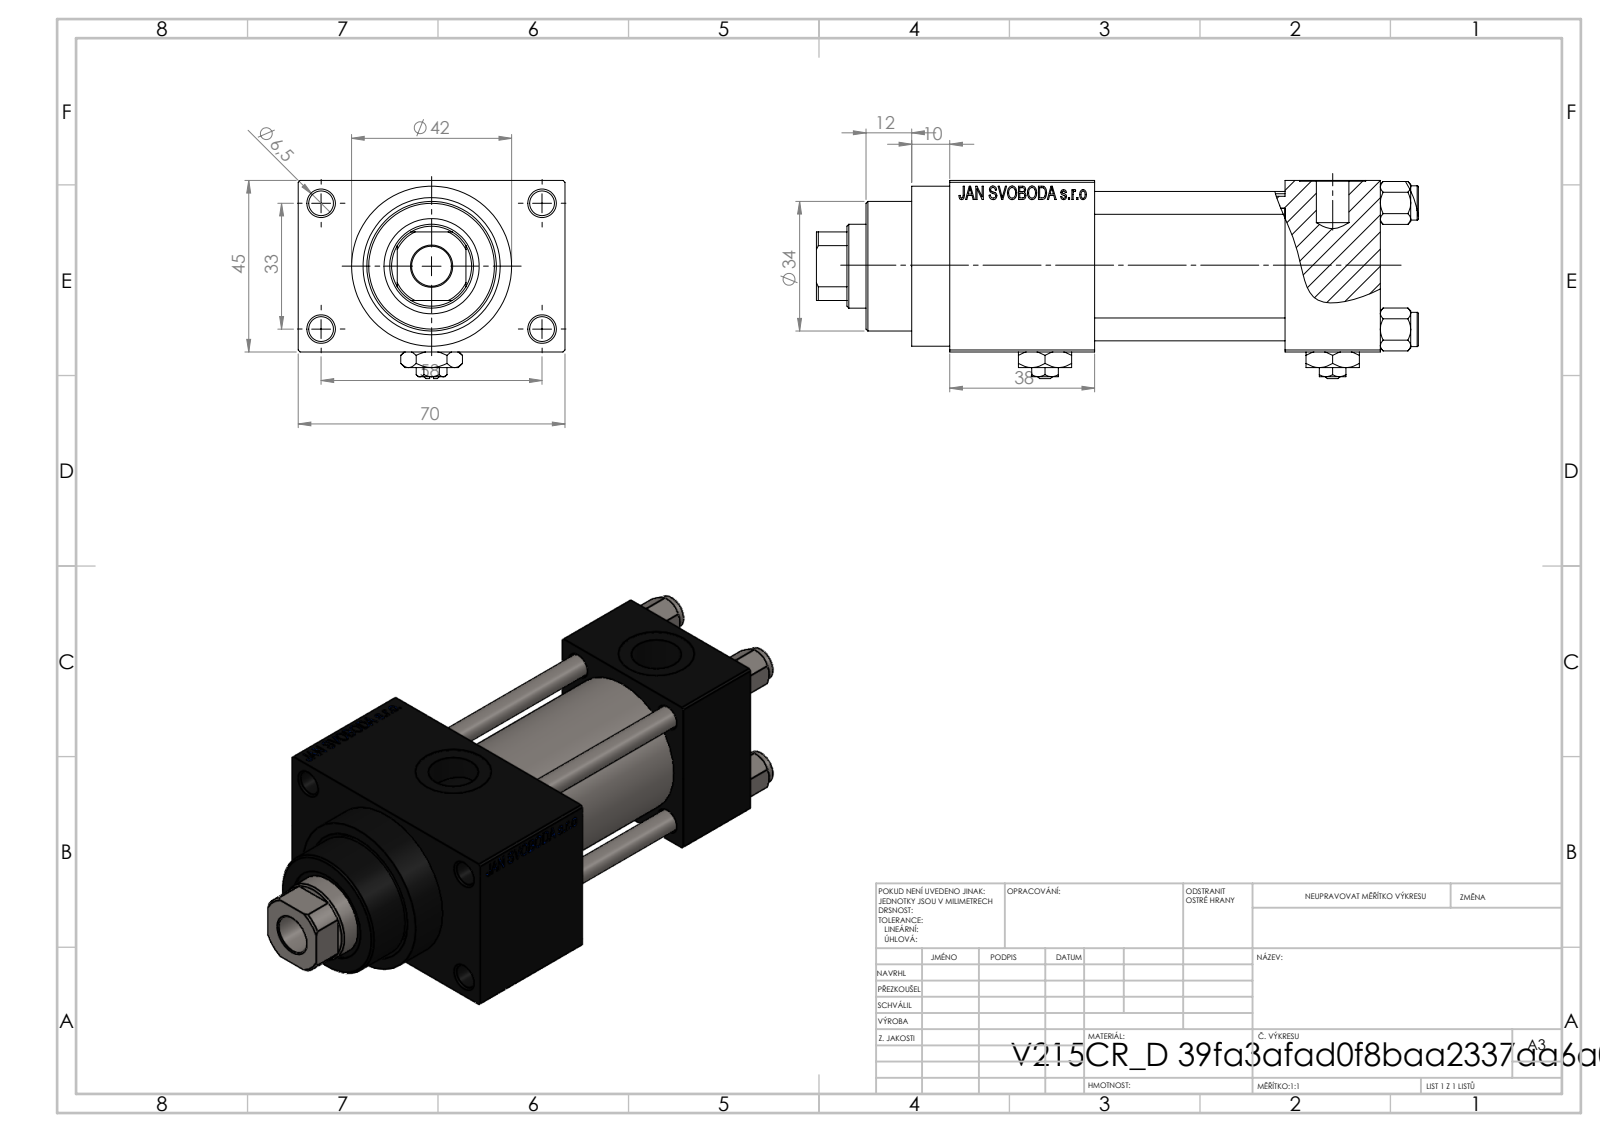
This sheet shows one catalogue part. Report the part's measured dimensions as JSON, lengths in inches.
{"part_name": "Zatka_pro_OIL_PORT; V215CR_VCP_D; V215CR_D_TYCINKA; NUT_M5_D (+2 more)", "step_written_by": "SolidWorks 2019 (CONFIG_CONTROL_DESIGN)", "units": "inches", "bodies": {"solids": 13, "faces": 1204, "planar": 542, "cylindrical": 100, "other": 562}, "overall_size": [6.22, 2.756, 2.047], "volume_in3": 14.84, "surface_area_in2": 125.7, "round_holes": [[0.236, 4], [0.256, 4], [0.276, 2], [0.518, 2], [0.787, 2], [0.413, 1], [0.866, 1], [0.945, 1], [0.984, 1], [1.26, 1], [1.299, 1]], "round_bosses_or_shafts": [[0.354, 4], [1.654, 1], [1.496, 1], [1.339, 1]], "partial_cylinders_radius": [[0.413, 1]], "face_to_face_distances": [1.772, 0.984, 0.492, 2.264, 1.969, 2.953, 3.465, 2.756, 1.496, 4.449], "hole_center_spacings": [0.488, 0.924, 1.307, 1.314, 1.392, 1.795, 2.219, 1.299]}
